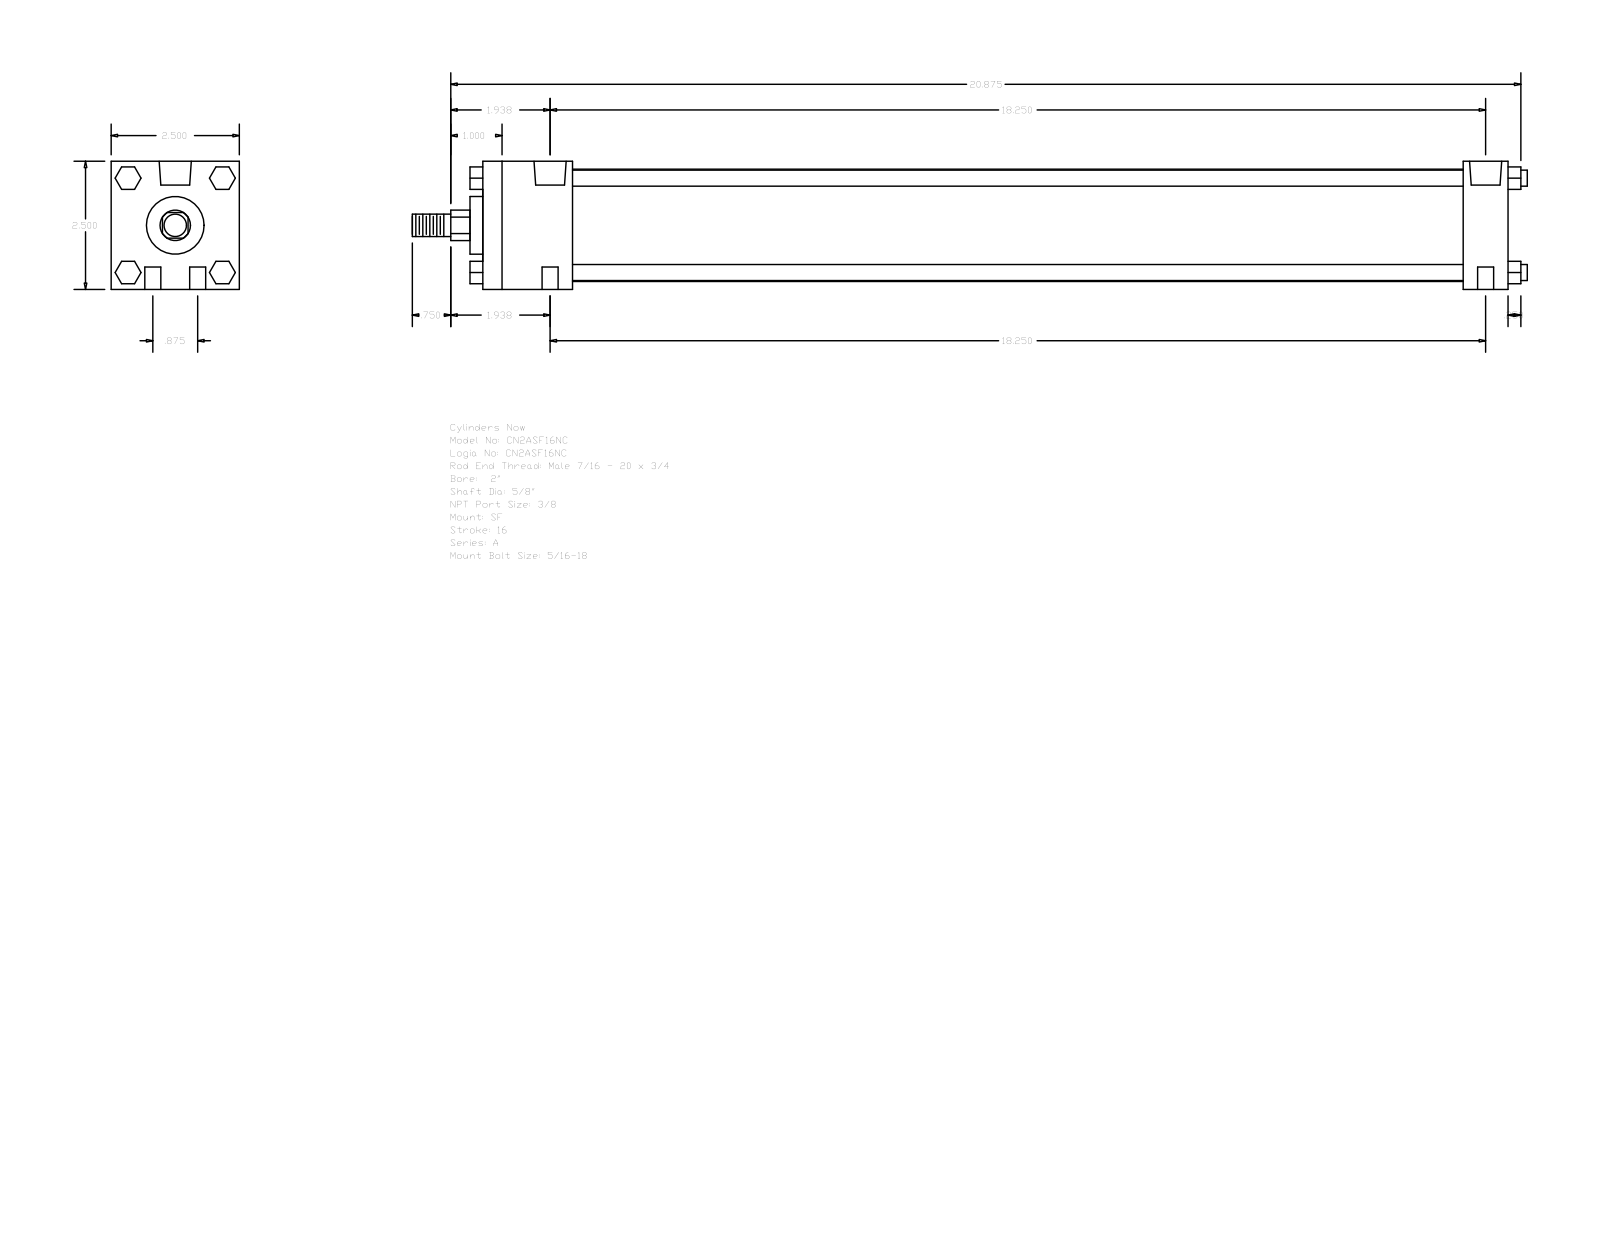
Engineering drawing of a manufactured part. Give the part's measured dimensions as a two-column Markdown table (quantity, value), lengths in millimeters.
| quantity | value |
| --- | --- |
| part name | A_SF__0200_0.625 |
| STEP written by | GSSL Pune (CONFIG_CONTROL_DESIGN) |
| units | millimeters |
| bodies | 0 solids, 124 faces (94 planar, 30 cylindrical, 0 other) |
| overall size | 552.45 × 63.5 × 63.5 |
| round holes (diameter × count) | 7.94 × 4, 5.56 × 2, 15.93 × 2 |
| round bosses / shafts (diameter × count) | 7.94 × 4, 55.63 × 1, 28.57 × 1, 15.88 × 1, 11.11 × 1 |
| partial cylindrical surfaces (radius × count) | 7.54 × 1 |
| main face-to-face distances | 63.5, 508, 485.77, 22.23, 44.45, 441.32, 463.55, 6.35, 514.35, 50.8 |
| hole center spacings | 11.11, 463.68, 463.55, 22.22, 464.08, 455.6 |
